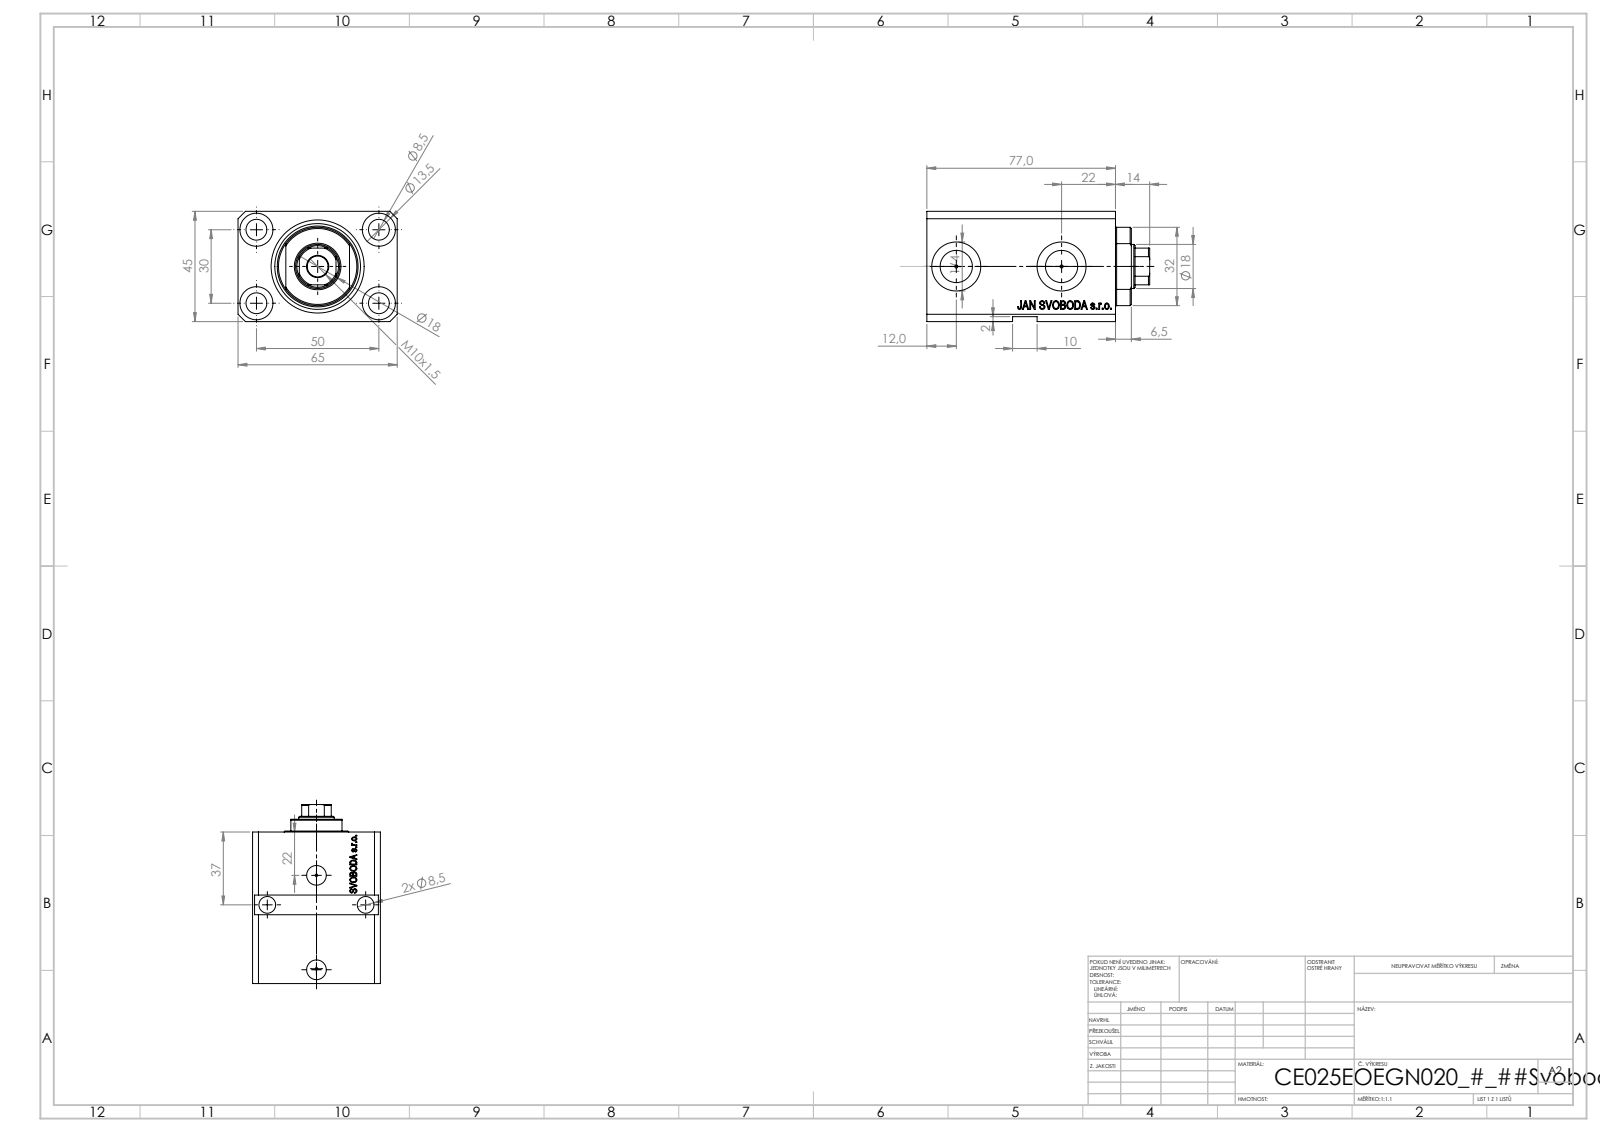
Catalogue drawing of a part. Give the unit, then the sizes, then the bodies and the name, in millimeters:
Units: millimetres
Overall size (bounding box): 91 × 65 × 45
Round holes (diameter × count): ⌀8.5 ×7, ⌀1.25 ×4, ⌀13.5 ×4, ⌀10 ×2, ⌀13.16 ×2, ⌀20 ×2, ⌀18 ×1, ⌀25 ×1, ⌀38 ×1
Partial cylindrical surfaces — rounded edges, fillets, slot ends (radius × count): R8.5 ×1, R16 ×1
Main face-to-face distances: 45, 65, 63, 14, 77, 6.9, 56.1, 70.1, 43, 9
Hole centre spacings: 29.15, 50, 30, 40.98, 41.4, 58.31, 0.53, 43
Volume: 191 714 mm³ · Surface area: 52 259 mm²
Bodies: 3 solids, 897 faces (435 planar, 84 cylindrical, 378 other)
Part name (STEP PRODUCT): V250CE_VC_E; V250CE_E_Body; V250CE_C_VCP
STEP written by: SolidWorks 2019 (CONFIG_CONTROL_DESIGN)
